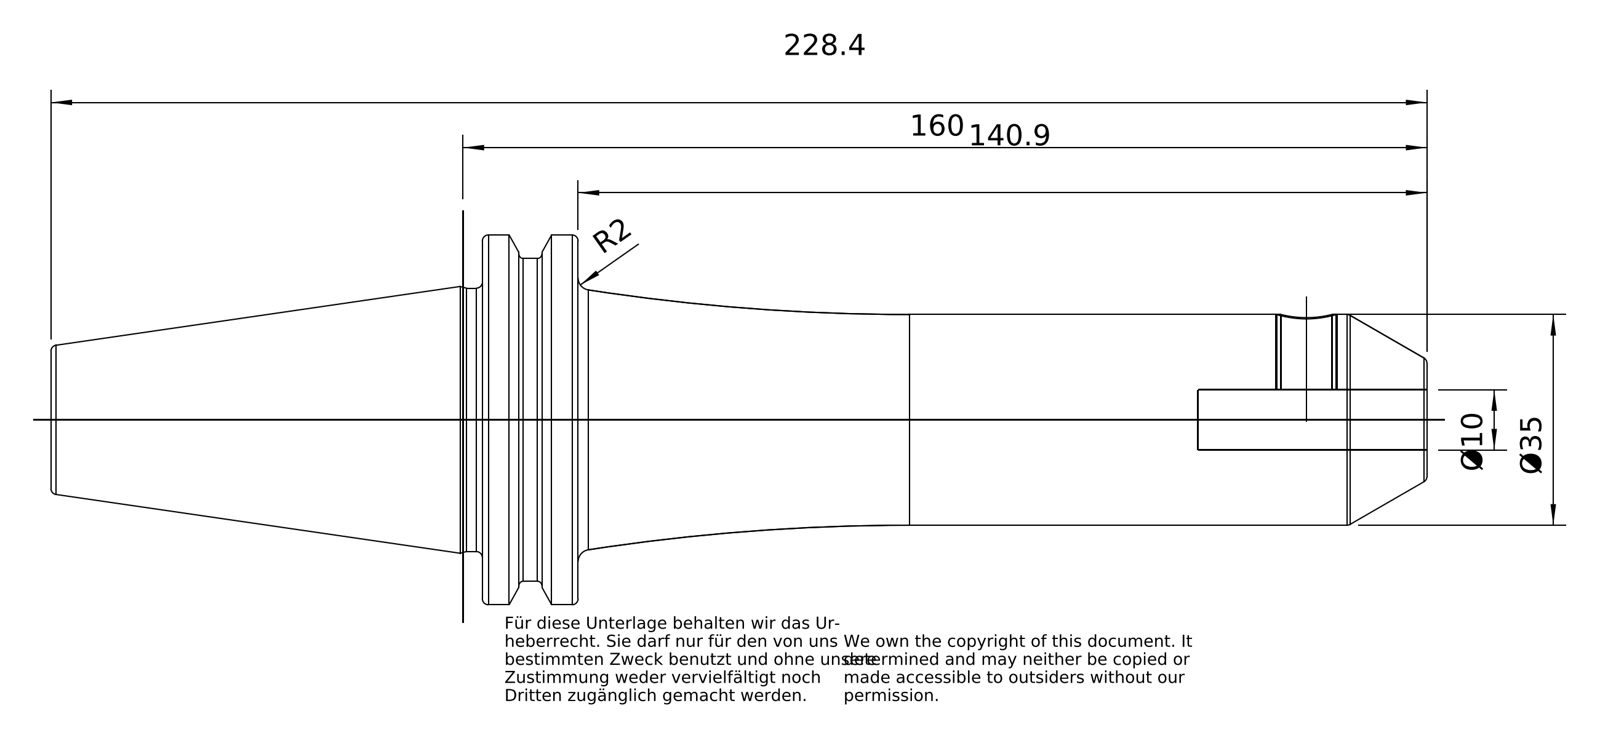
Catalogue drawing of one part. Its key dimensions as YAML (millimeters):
part_name: "40-302-10"
step_written_by: "PRO/ENGINEER BY PARAMETRIC TECHNOLOGY CORPORATION, 2010430 (CONFIG_CONTROL_DESIGN)"
units: millimeters
bodies: {solids: 1, faces: 101, planar: 21, cylindrical: 28, other: 52}
overall_size: [228.25, 63.52, 61.42]
volume: 242495
surface_area: 36455
round_holes:
  - {diameter: 10, count: 2}
  - {diameter: 8.5, count: 1}
  - {diameter: 13.84, count: 1}
  - {diameter: 17.01, count: 1}
  - {diameter: 17.5, count: 1}
round_bosses_or_shafts:
  - {diameter: 43.75, count: 1}
  - {diameter: 35, count: 1}
  - {diameter: 16.01, count: 1}
partial_cylinders:
  - {radius: 1.35, count: 1}
  - {radius: 28, count: 1}
  - {radius: 31.76, count: 1}
face_to_face_distances: [15.85, 47.4, 156.8, 140.95, 16.2, 71.45, 87.3, 228.25, 190.25, 118.8]
